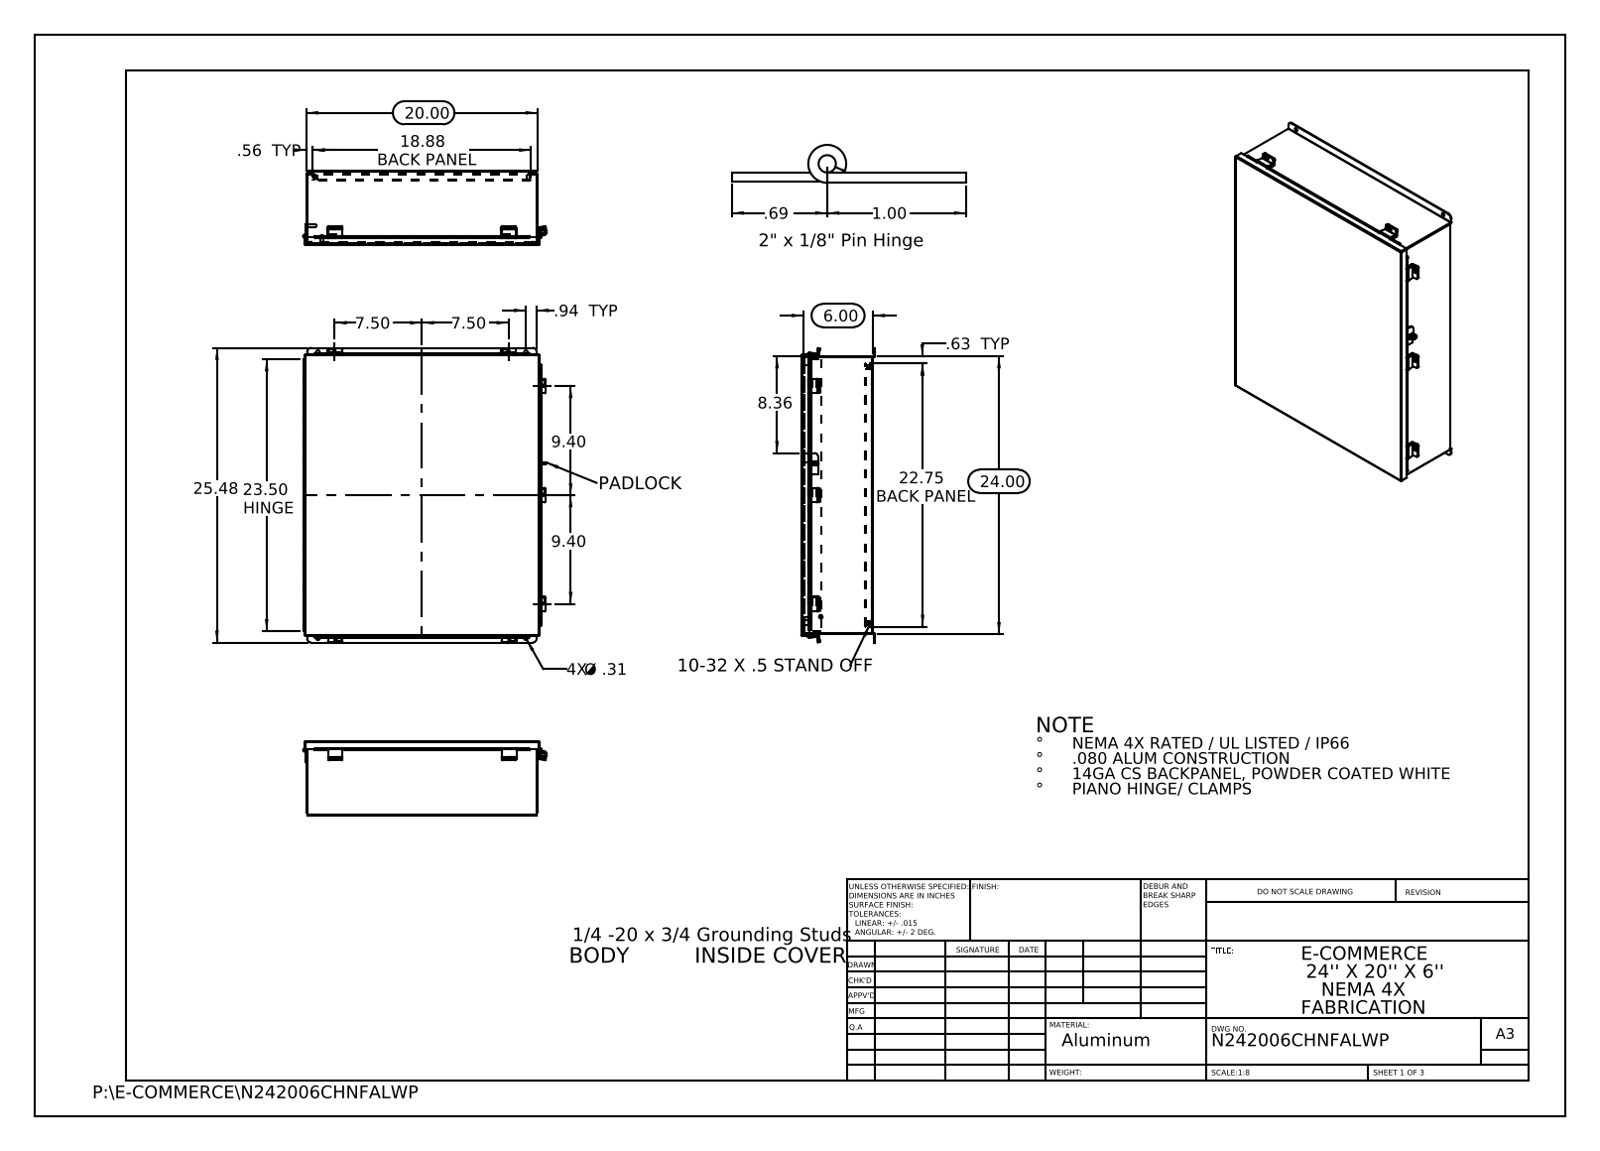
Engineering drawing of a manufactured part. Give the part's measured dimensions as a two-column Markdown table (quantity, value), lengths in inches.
| quantity | value |
| --- | --- |
| part name | N242006CHNFALWP; N242006CHNFALWP Hinge Cover Side JIC; N242006CHNFALWP HW-CD-S-25020-034; N242006CHNFALWP Hinge Body Side (+8 more) |
| STEP written by | SolidWorks 2013 (CONFIG_CONTROL_DESIGN) |
| units | inches |
| bodies | 29 solids, 1056 faces (651 planar, 385 cylindrical, 20 other) |
| overall size | 25.476 × 21.072 × 6.39 |
| volume | 157.9 in³ |
| surface area | 4 279 in² |
| round holes (diameter × count) | 0.25 × 11, 0.187 × 4, 0.312 × 4, 0.125 × 1, 0.125 × 1, 0.373 × 1, 0.375 × 1 |
| round bosses / shafts (diameter × count) | 0.313 × 4, 0.315 × 2, 0.236 × 2, 0.273 × 1, 0.25 × 1 |
| partial cylindrical surfaces (radius × count) | 0.125 × 24, 0.133 × 14, 0.013 × 13, 0.009 × 12, 0.088 × 12, 0.083 × 6, 0.1 × 6, 0.375 × 4 |
| main face-to-face distances | 0.075, 6.128, 6.053, 6.203, 0.074, 5.628, 0.575, 0.5, 5.553, 0.649 |
| hole center spacings | 1.315, 18.222, 23.427, 29.65, 9.425, 15, 17.976, 18.375 |
